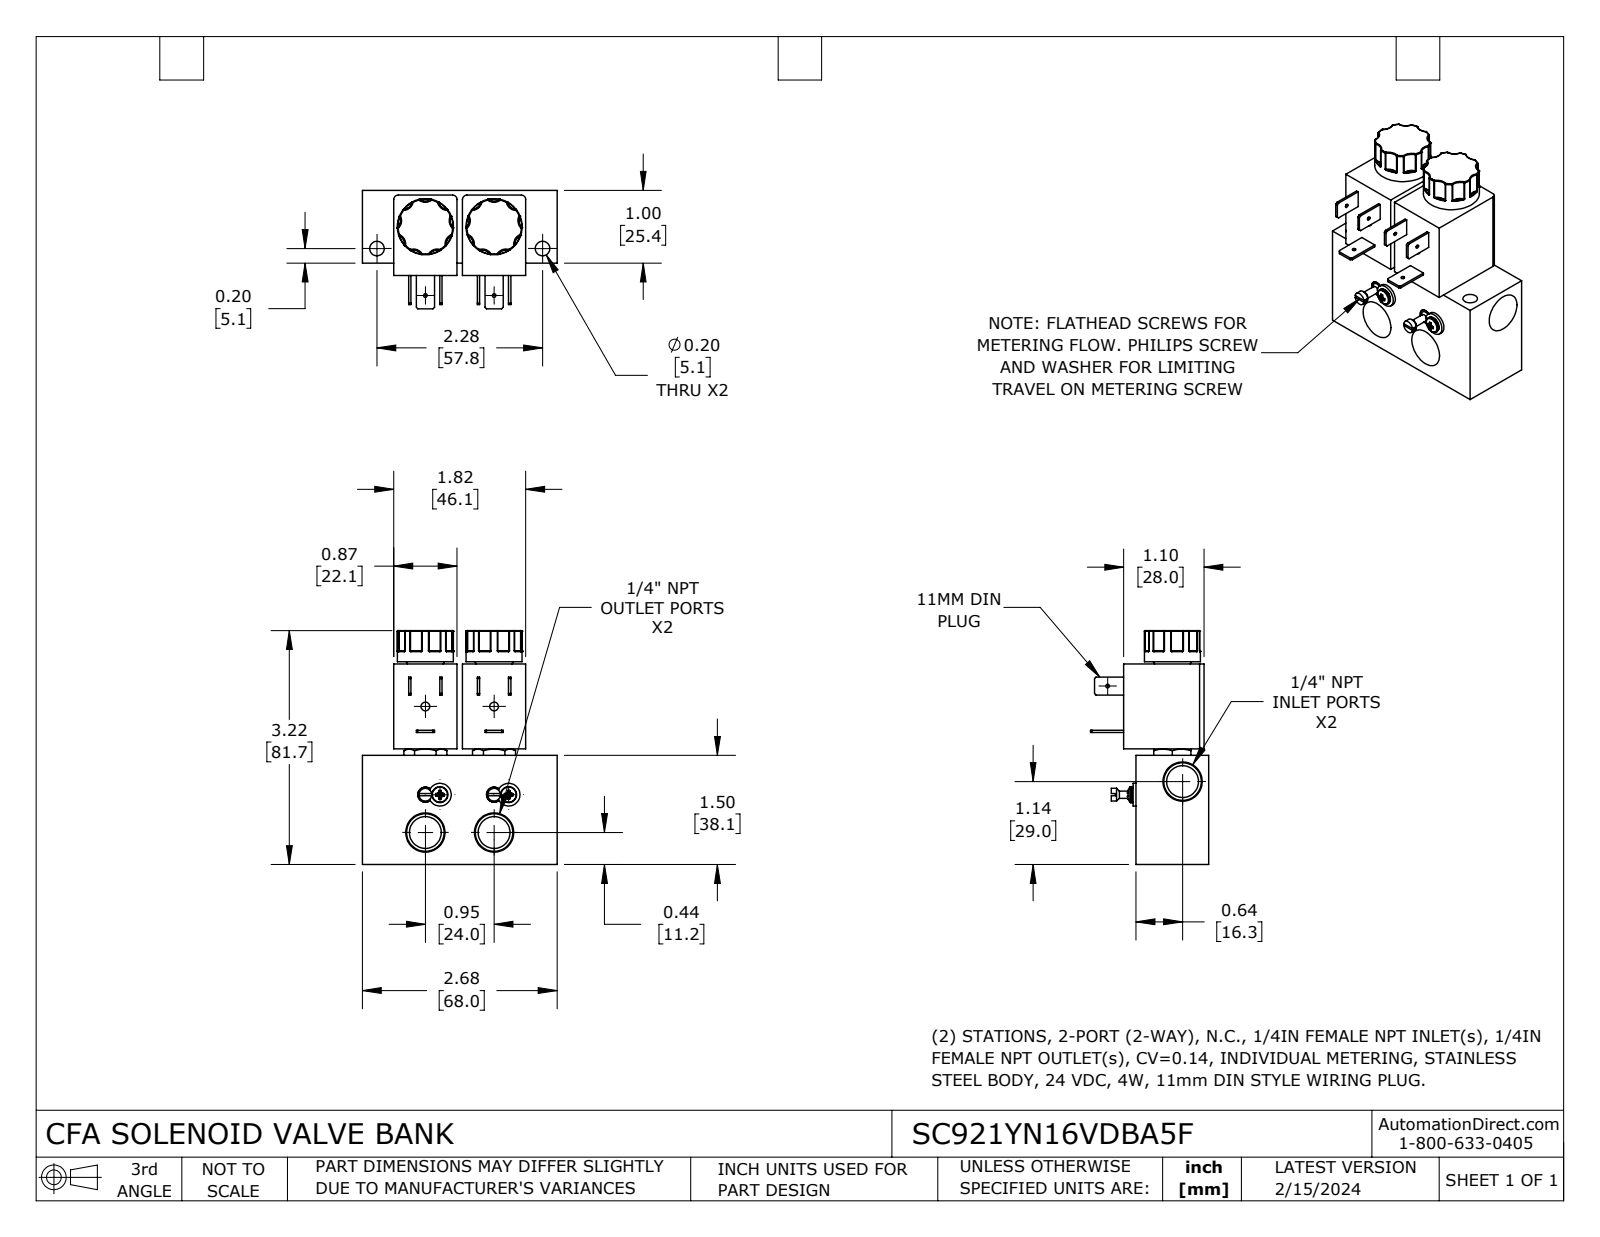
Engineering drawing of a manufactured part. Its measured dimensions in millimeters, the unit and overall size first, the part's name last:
Units: millimetres
Overall size (bounding box): 81.7 × 68 × 41.3
Round holes (diameter × count): ⌀1.3 ×3, ⌀11.1 ×3, ⌀3 ×2, ⌀5.1 ×2, ⌀5.3 ×2
Round bosses / shafts (diameter × count): ⌀19.6 ×2, ⌀7.9 ×2, ⌀5.6 ×2, ⌀5.2 ×2, ⌀4.4 ×2, ⌀2.6 ×2, ⌀2.5 ×2
Partial cylindrical surfaces — rounded edges, fillets, slot ends (radius × count): R0.3 ×36, R3.4 ×18, R1.5 ×4, R7.8 ×1
Main face-to-face distances: 25.4, 24, 10.9, 33, 35, 57, 22.1, 38.1, 29.7, 4.3
Hole centre spacings: 24, 13.2, 23.6, 27.4, 30.8, 39, 44, 44.1
Volume: 100 900 mm³ · Surface area: 25 980 mm²
Bodies: 1 solid, 589 faces (156 planar, 152 cylindrical, 281 other)
Part name (STEP PRODUCT): SC921YN16VDBA5F
STEP written by: SolidWorks 2023 (CONFIG_CONTROL_DESIGN)
